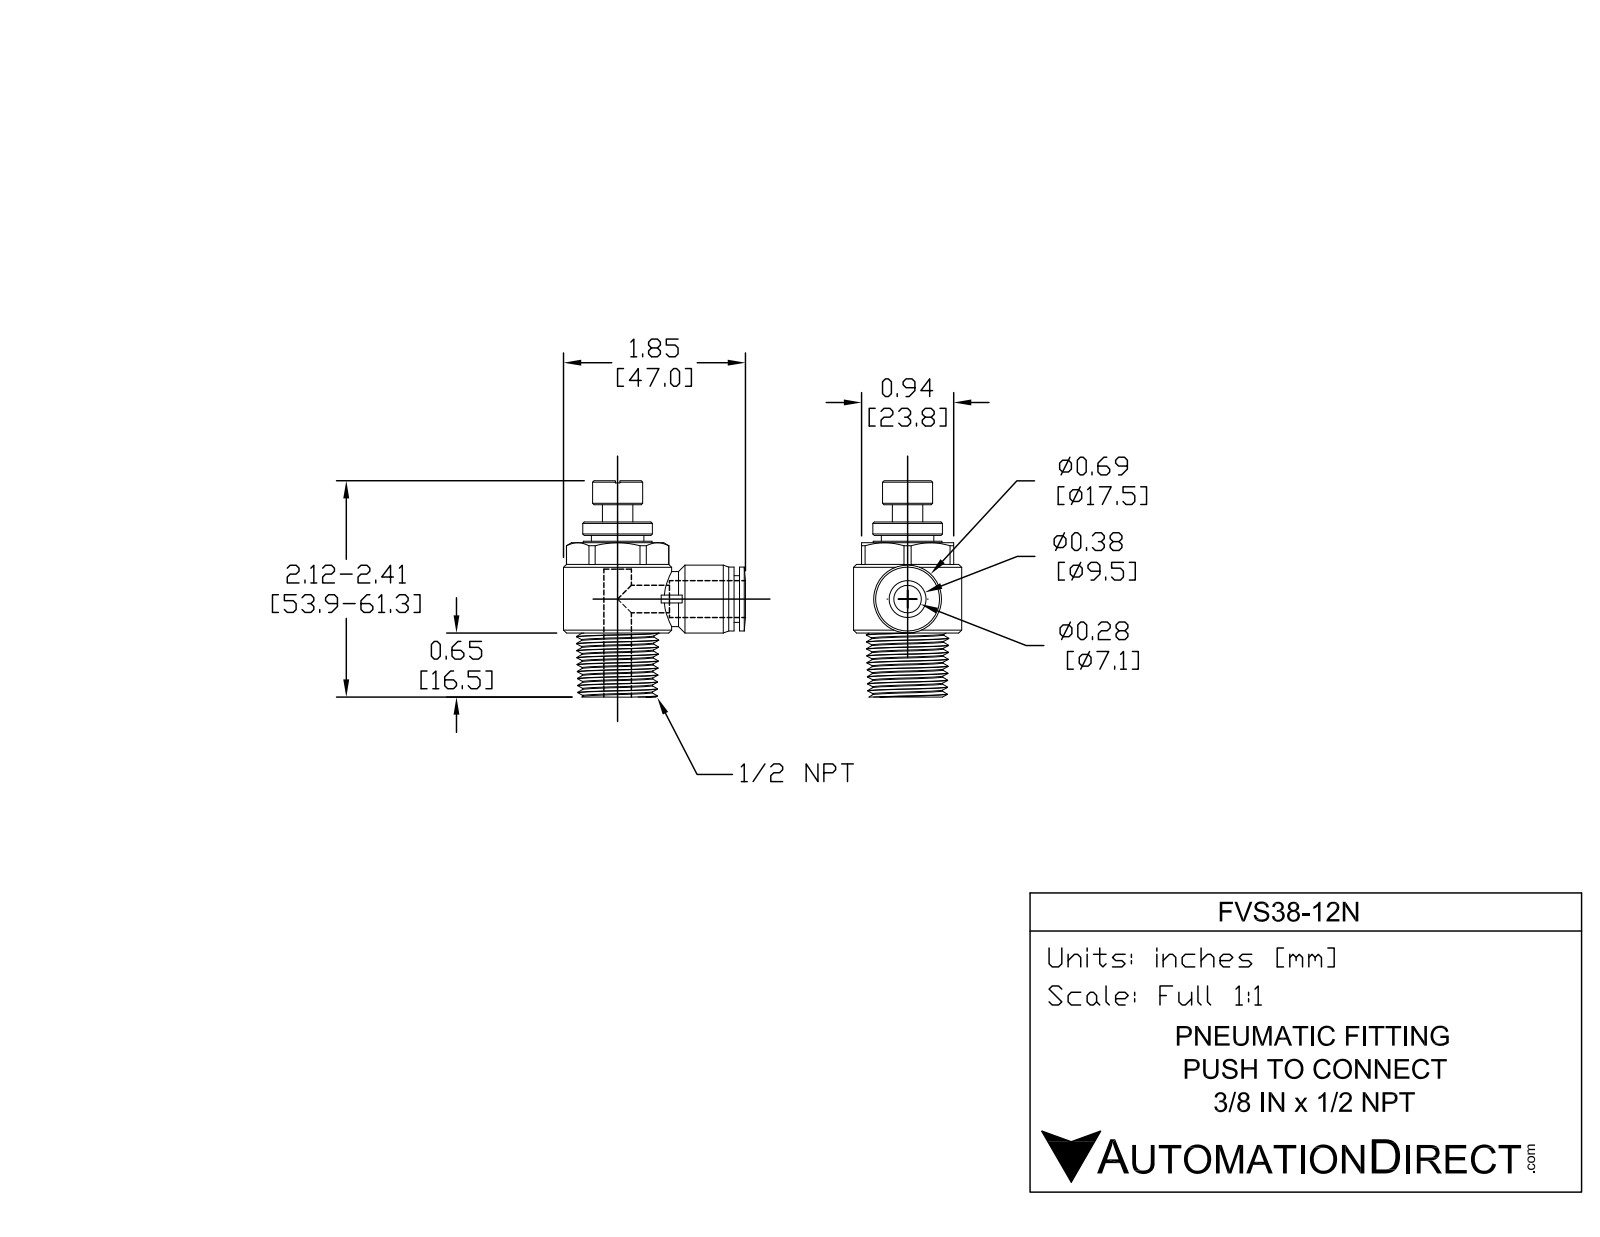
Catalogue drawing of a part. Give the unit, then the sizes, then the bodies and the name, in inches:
Units: inches
Overall size (bounding box): 2.413 × 1.858 × 1.102
Round holes (diameter × count): ⌀0.276 ×2, ⌀0.386 ×1
Round bosses / shafts (diameter × count): ⌀0.551 ×2, ⌀1.102 ×1, ⌀0.945 ×1, ⌀0.864 ×1, ⌀0.713 ×1, ⌀0.689 ×1, ⌀0.669 ×1, ⌀0.661 ×1
Partial cylindrical surfaces — rounded edges, fillets, slot ends (radius × count): R0.256 ×1, R0.354 ×1, R0.512 ×1
Main face-to-face distances: 1.622, 0.697, 0.925, 1.831, 1.134, 0.209, 0.945, 0.047, 0.996, 1.693
Volume: 1.431 in³ · Surface area: 12.77 in²
Bodies: 1 solid, 576 faces (259 planar, 149 cylindrical, 168 other)
Part name (STEP PRODUCT): FVS38-12N
STEP written by: SolidWorks 2015 (AUTOMOTIVE_DESIGN)
